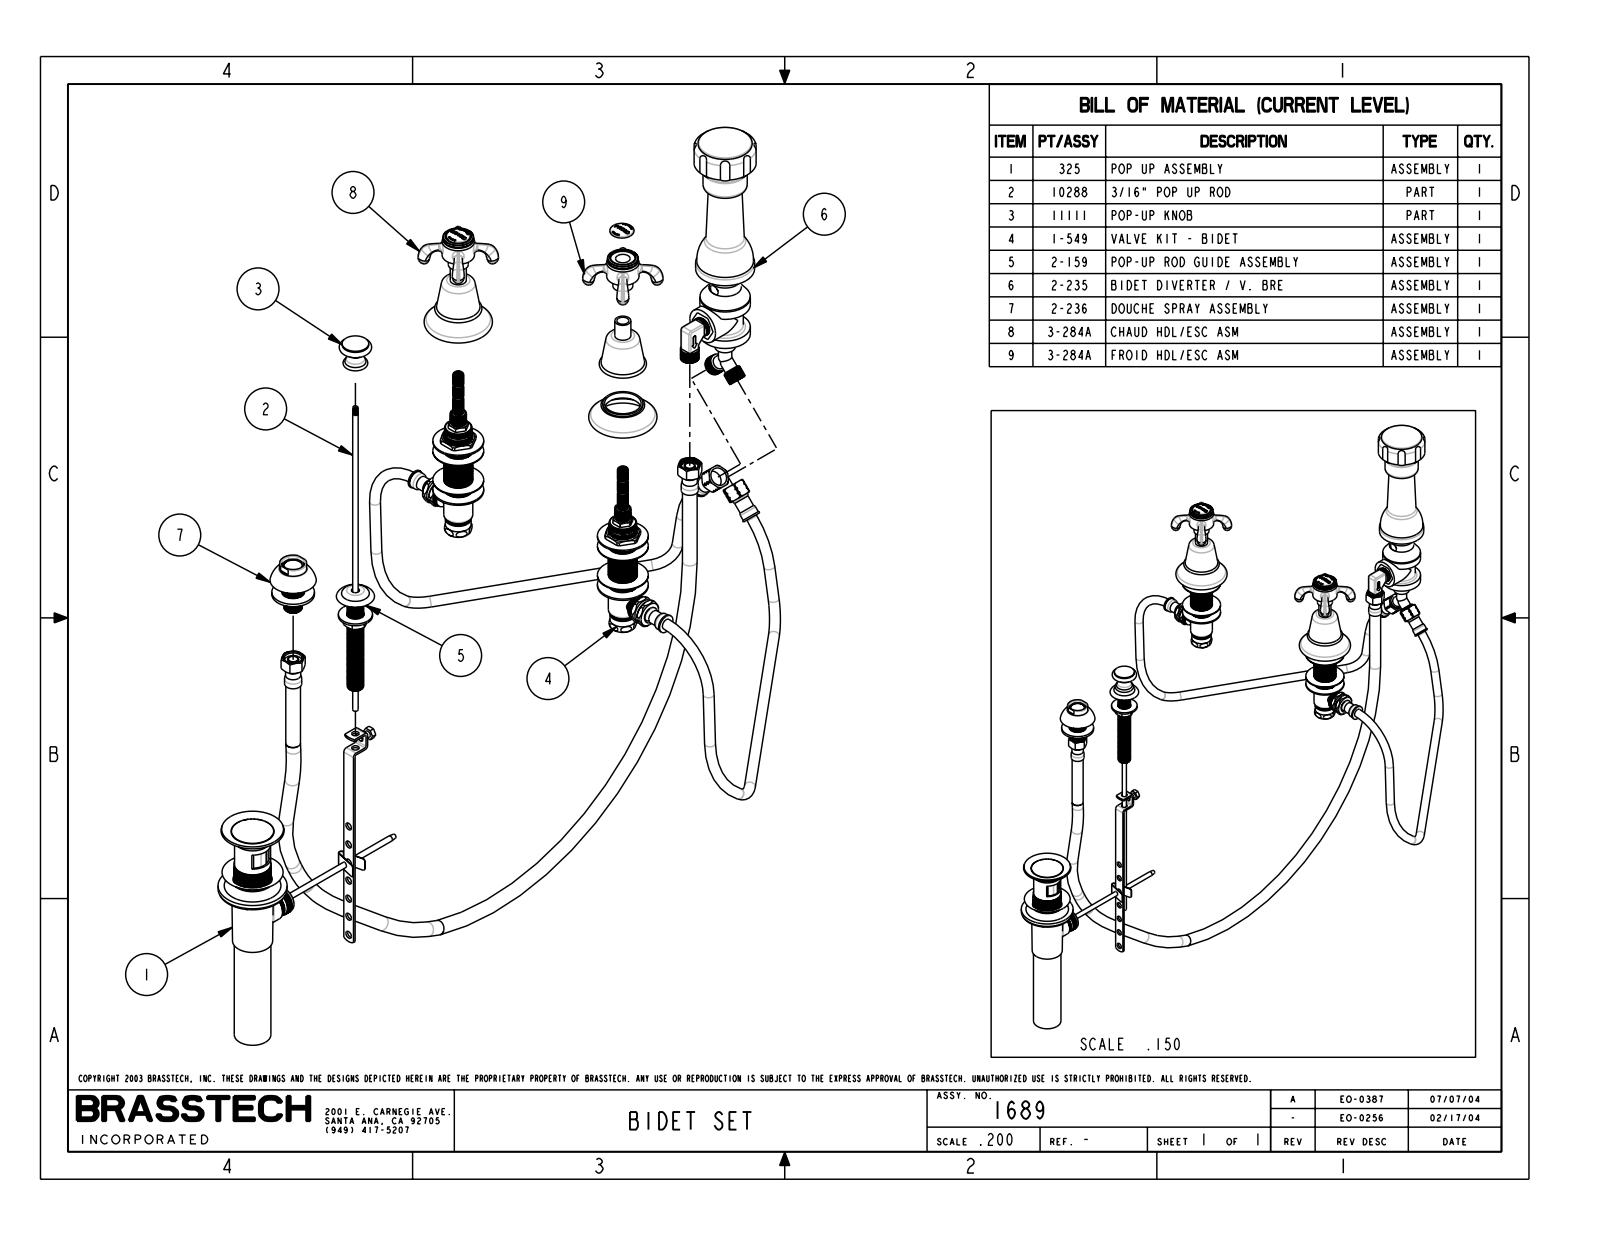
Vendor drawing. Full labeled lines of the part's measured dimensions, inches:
Part name (STEP PRODUCT): 1689_WEB
STEP written by: PRO/ENGINEER BY PARAMETRIC TECHNOLOGY CORPORATION, 2009300 (CONFIG_CONTROL_DESIGN)
Units: inches
Bodies: 0 solids, 599 faces (21 planar, 40 cylindrical, 538 other)
Overall size (bounding box): 22.856 × 10.35 × 5.353
Round bosses / shafts (diameter × count): ⌀1.115 ×2, ⌀1.055 ×2, ⌀0.687 ×2, ⌀0.553 ×2, ⌀2.025 ×1, ⌀1.52 ×1, ⌀0.926 ×1, ⌀0.915 ×1
Partial cylindrical surfaces — rounded edges, fillets, slot ends (radius × count): R0.21 ×8, R1.077 ×1
Main face-to-face distances: 3.468, 3.73, 0.262, 1.875, 1.593, 1.855, 2.53, 0.655, 0.938, 1.2
